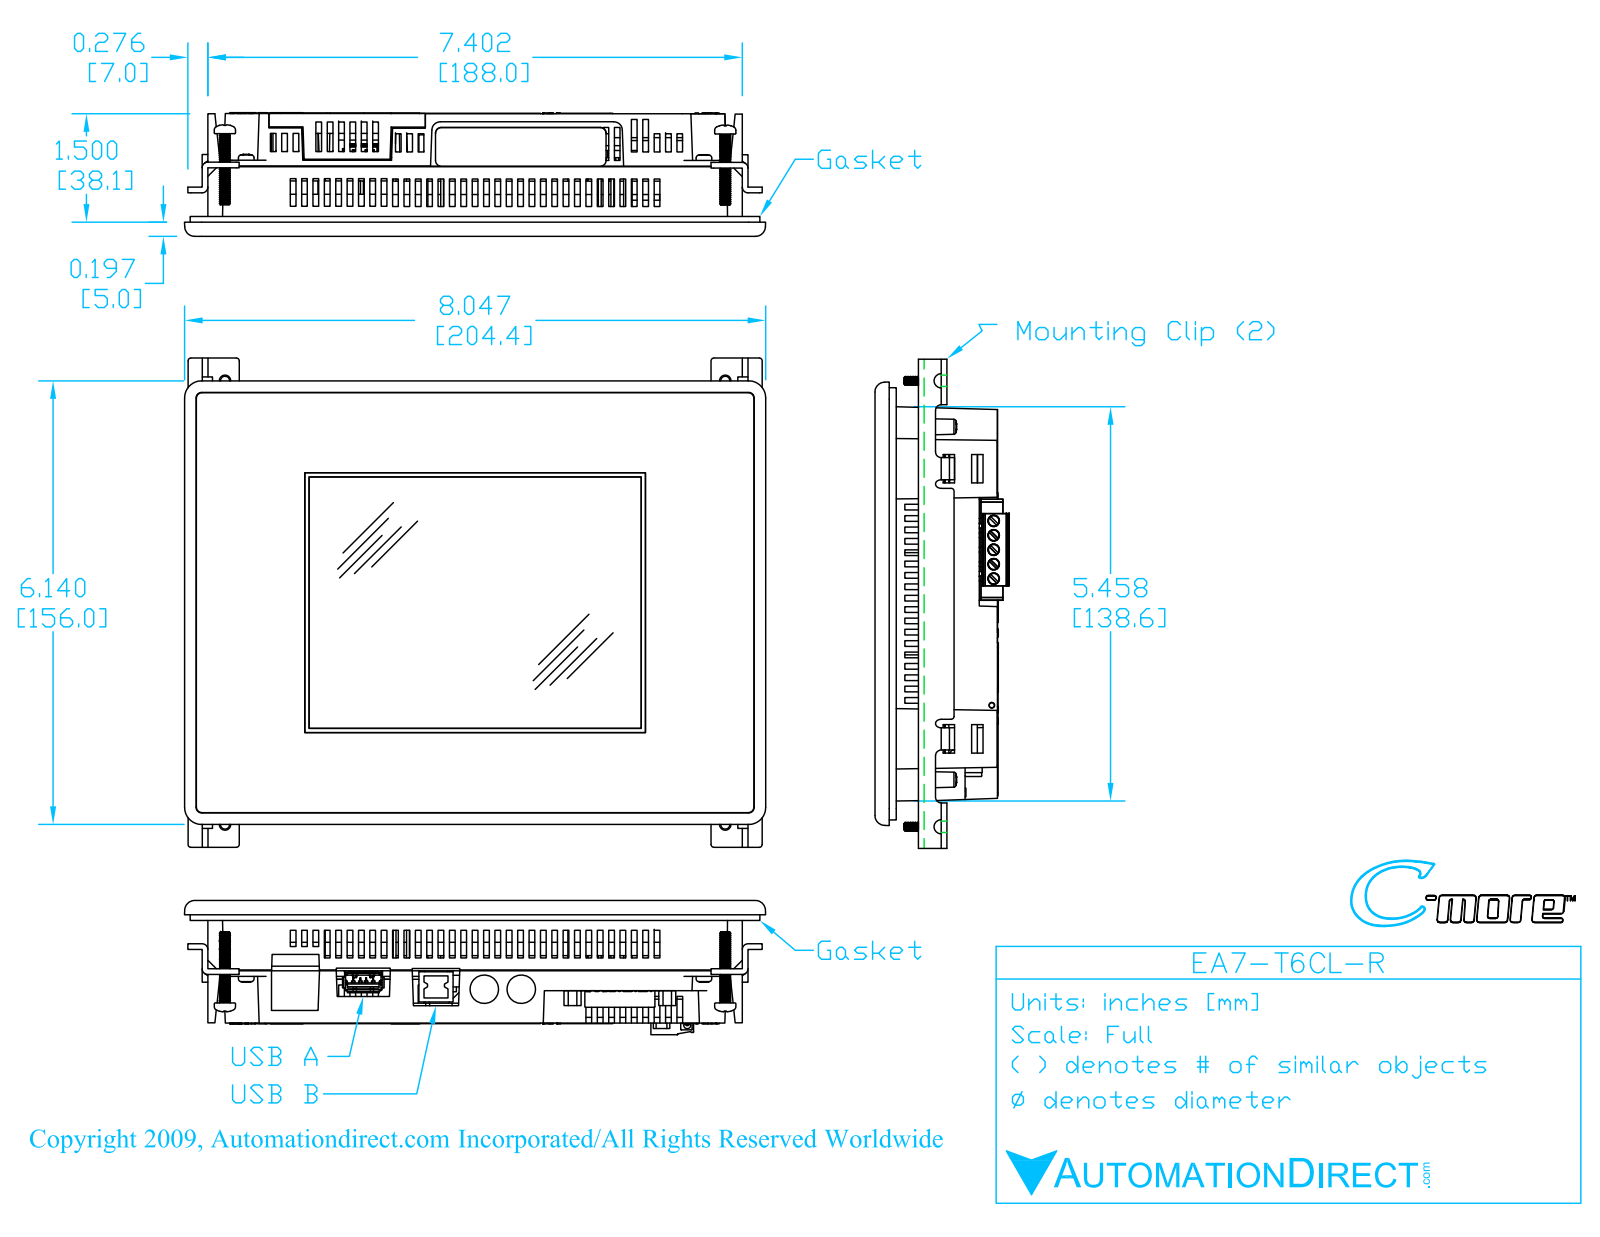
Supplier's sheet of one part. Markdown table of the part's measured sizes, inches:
| quantity | value |
| --- | --- |
| part name | EA7-T6CL-R |
| STEP written by | SolidWorks 2009 (AUTOMOTIVE_DESIGN) |
| units | inches |
| bodies | 1 solid, 483 faces (370 planar, 95 cylindrical, 18 other) |
| overall size | 8.047 × 6.142 × 1.856 |
| volume | 18.77 in³ |
| surface area | 311.6 in² |
| round holes (diameter × count) | 0.138 × 3, 0.38 × 2, 0.177 × 1 |
| round bosses / shafts (diameter × count) | 0.315 × 1, 0.256 × 1 |
| partial cylindrical surfaces (radius × count) | 0.079 × 20, 0.039 × 16, 0.121 × 5, 0.141 × 5, 0.098 × 4, 0.157 × 4, 0.157 × 4, 0.236 × 4 |
| main face-to-face distances | 0.12, 0.077, 1.62, 1.697, 1.5, 1.577, 5.337, 6.869, 5.457, 1.346 |
| hole center spacings | 0.504, 1.195 |
